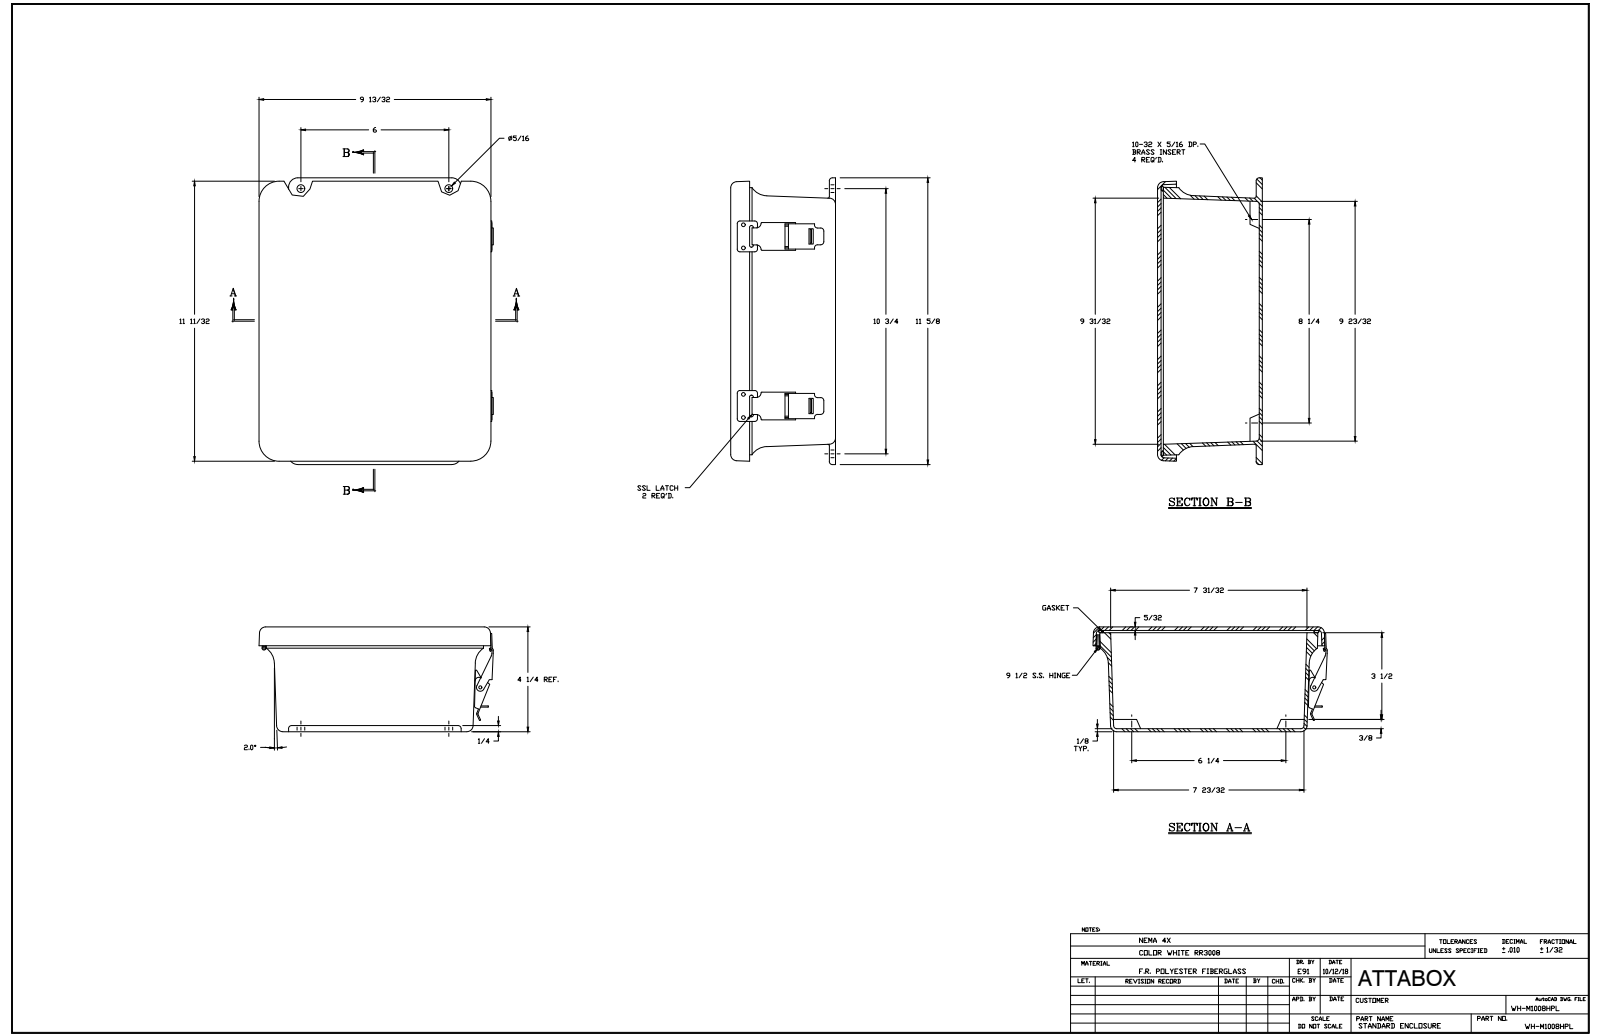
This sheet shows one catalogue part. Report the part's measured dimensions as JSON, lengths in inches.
{"part_name": "WH-M1008HPL", "step_written_by": "SolidWorks 2018 (AUTOMOTIVE_DESIGN)", "units": "inches", "bodies": {"solids": 38, "faces": 939, "planar": 399, "cylindrical": 393, "other": 147}, "overall_size": [11.625, 9.529, 4.234], "volume_in3": 61.27, "surface_area_in2": 837.7, "round_holes": [[0.14, 20], [0.104, 8], [0.131, 8], [0.152, 5], [0.13, 4], [0.156, 4], [0.218, 4], [0.135, 2], [0.375, 2], [0.085, 1], [0.085, 1]], "round_bosses_or_shafts": [[0.125, 12], [0.25, 8], [0.27, 4], [0.125, 4], [0.3, 1], [0.17, 1], [0.155, 1], [0.155, 1]], "partial_cylinders_radius": [[0.015, 20], [0.031, 20], [0.125, 20], [0.045, 16], [0.03, 12], [0.023, 8], [0.25, 8], [0.06, 6]], "face_to_face_distances": [0.142, 4.092, 4.233, 0.125, 3.967, 4.109, 0.12, 3.89, 4.015, 0.077], "hole_center_spacings": [7, 7.04, 0.937, 6, 0.75, 3, 0.25, 0.75]}
